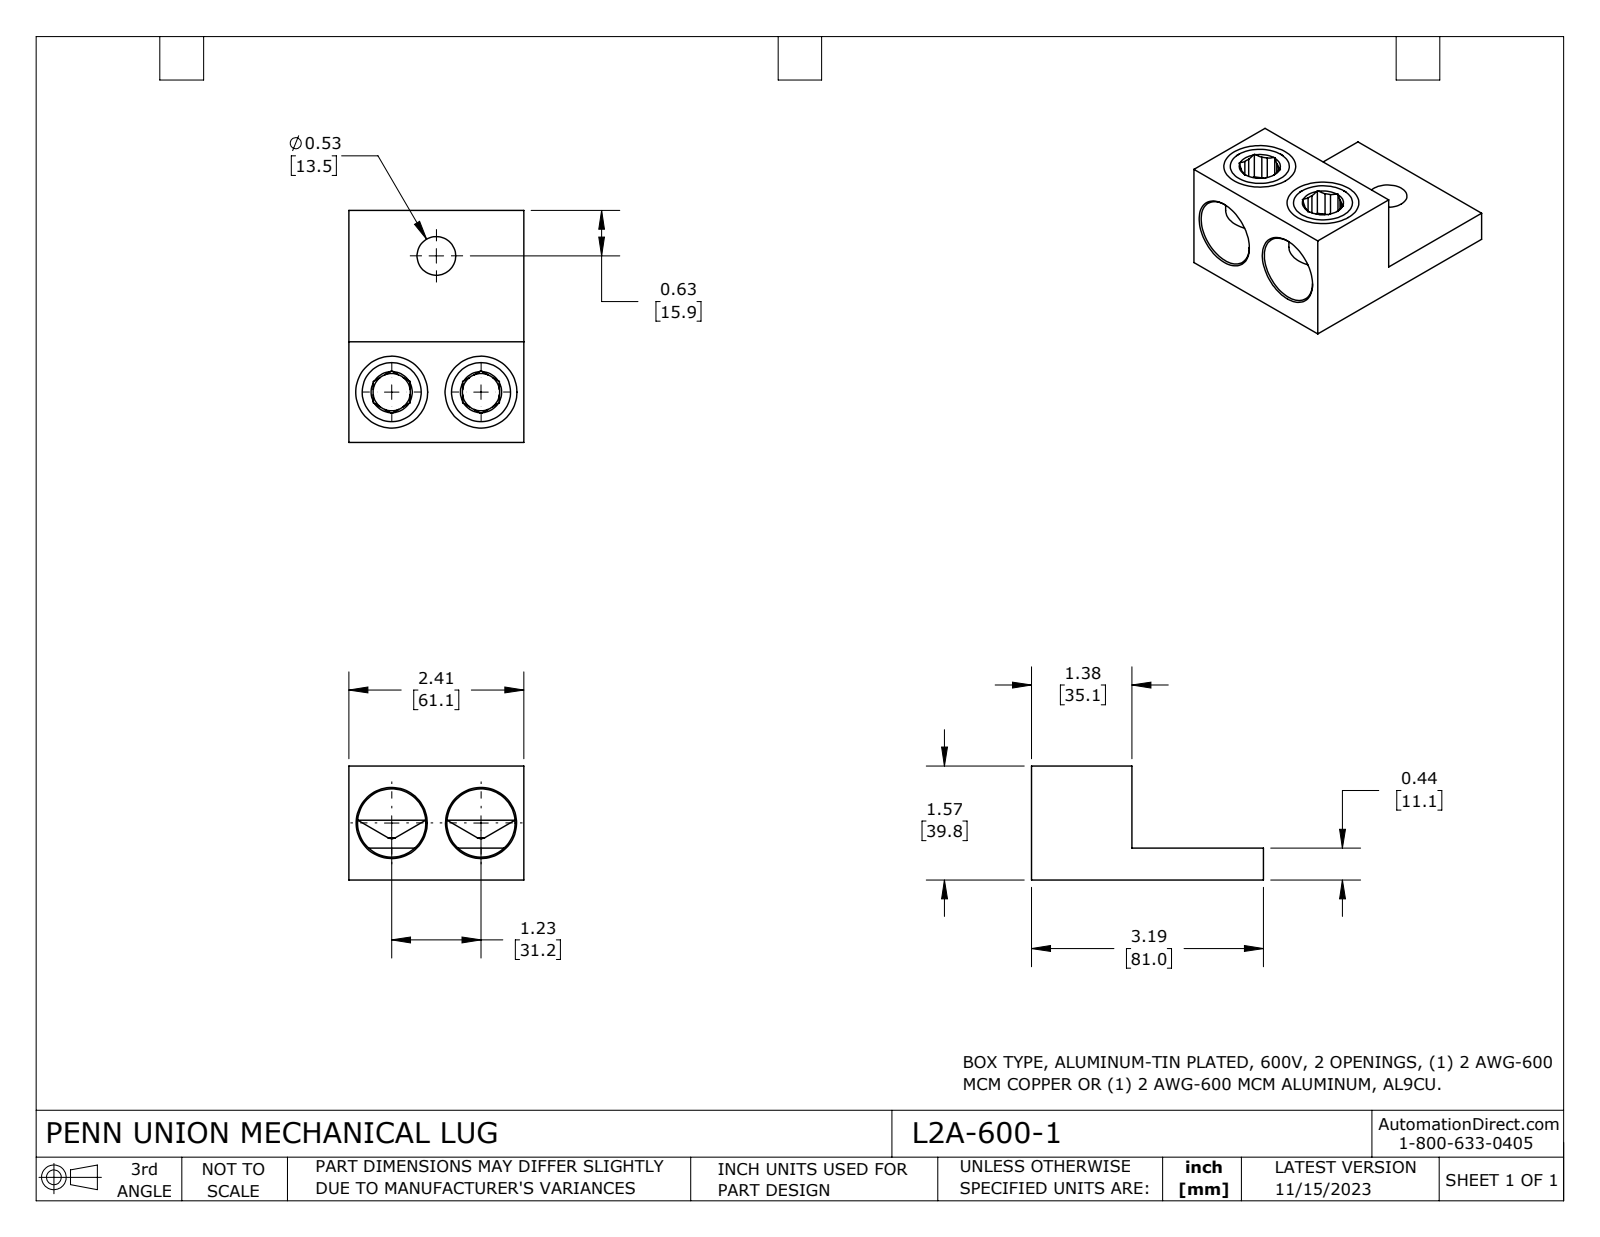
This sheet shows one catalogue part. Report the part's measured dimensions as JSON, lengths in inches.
{"part_name": "L2A-600-1", "step_written_by": "SolidWorks 2023 (CONFIG_CONTROL_DESIGN)", "units": "inches", "bodies": {"solids": 3, "faces": 102, "planar": 48, "cylindrical": 18, "other": 36}, "overall_size": [3.189, 2.406, 1.567], "volume_in3": 5.549, "surface_area_in2": 43.15, "round_holes": [[0.512, 2], [0.87, 2], [0.938, 2], [0.531, 1]], "round_bosses_or_shafts": [[0.937, 2]], "face_to_face_distances": [0.437, 2.406, 1.567, 1.13, 1.382, 3.189, 1.807, 0.614, 0.506, 0.335], "hole_center_spacings": [1.228, 1.97]}
